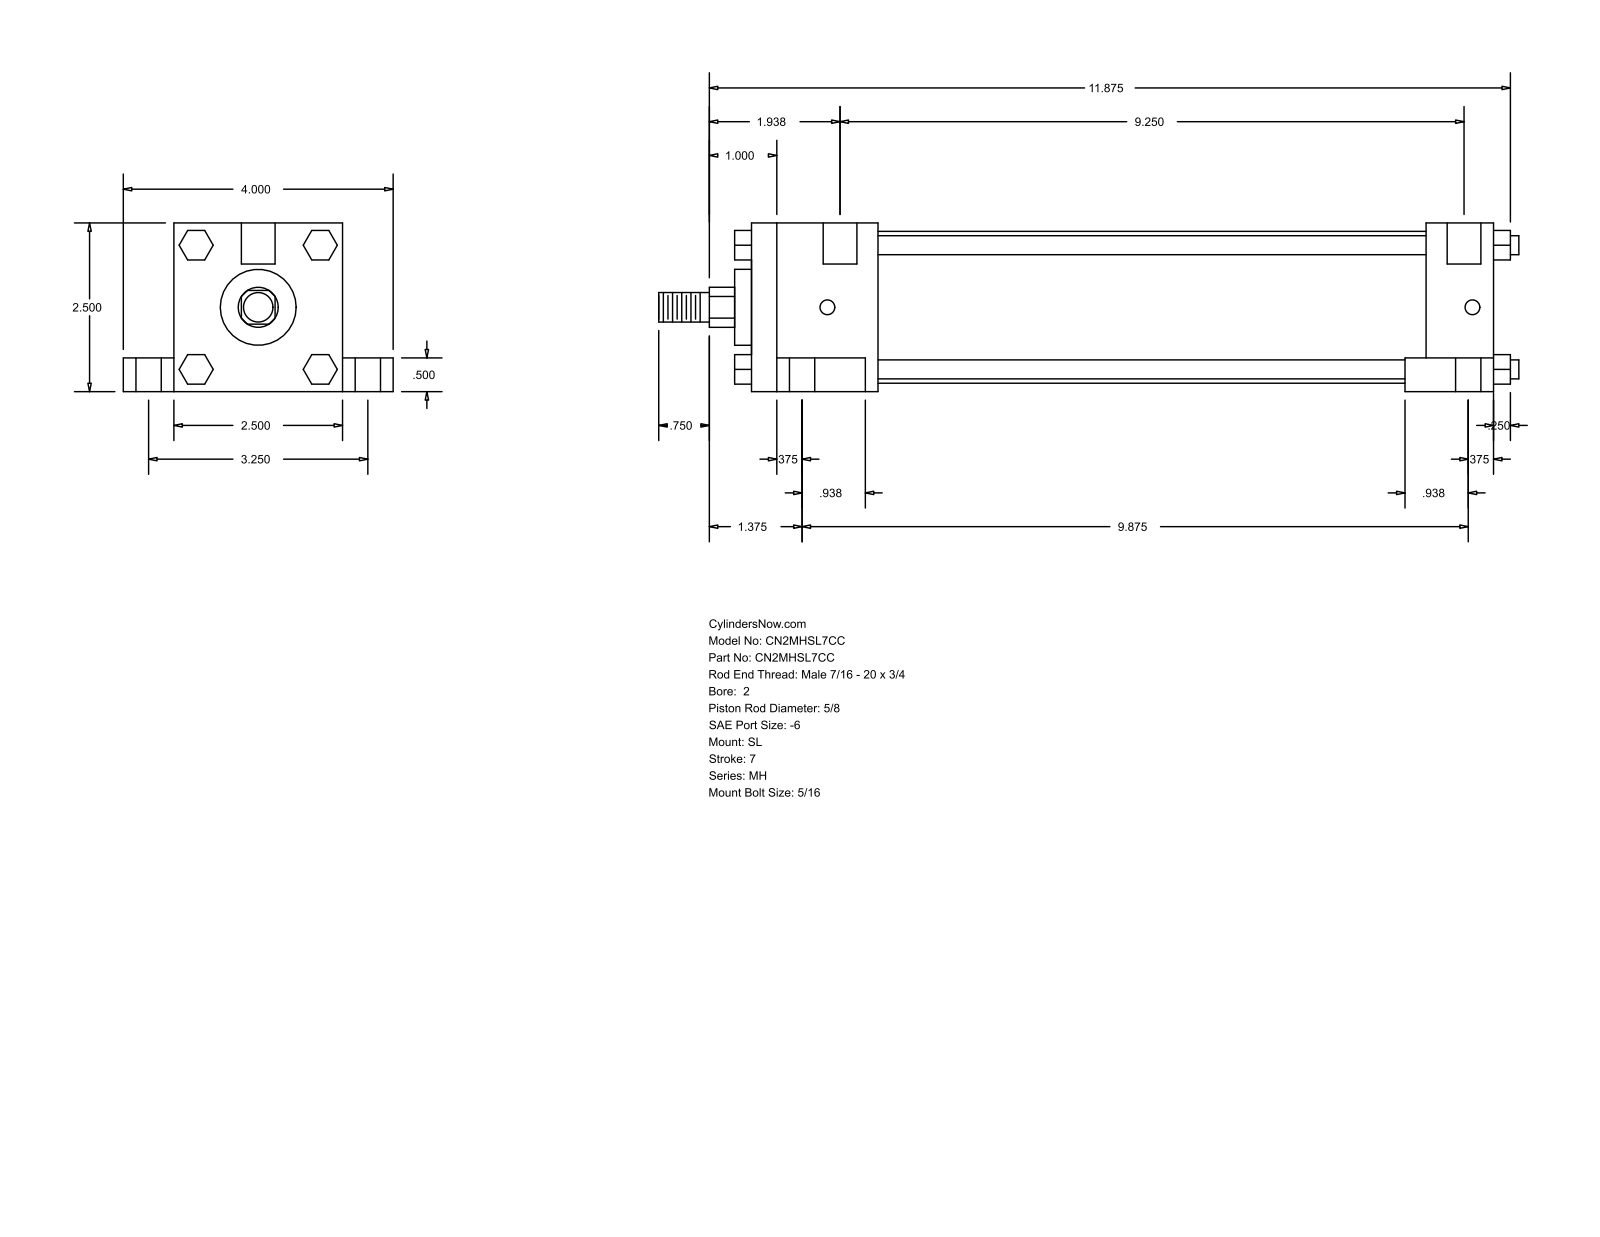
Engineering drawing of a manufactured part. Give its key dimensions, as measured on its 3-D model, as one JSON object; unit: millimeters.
{"part_name": "MH_SL__0200_0.625", "step_written_by": "GSSL Pune (CONFIG_CONTROL_DESIGN)", "units": "millimeters", "bodies": {"solids": 0, "faces": 148, "planar": 112, "cylindrical": 36, "other": 0}, "overall_size": [323.85, 101.6, 63.5], "round_holes": [[5.56, 4], [9.53, 4], [15.88, 4], [12.7, 2]], "round_bosses_or_shafts": [[7.14, 4], [57.15, 1], [28.57, 1], [15.88, 1], [11.11, 1]], "partial_cylinders_radius": [[7.54, 1]], "face_to_face_distances": [63.5, 279.39, 12.7, 19.05, 82.55, 50.8, 254, 25.39, 47.62, 206.38], "hole_center_spacings": [41.3, 42.36, 43.67, 82.54, 240.11, 242.89, 244.8, 250.83]}
